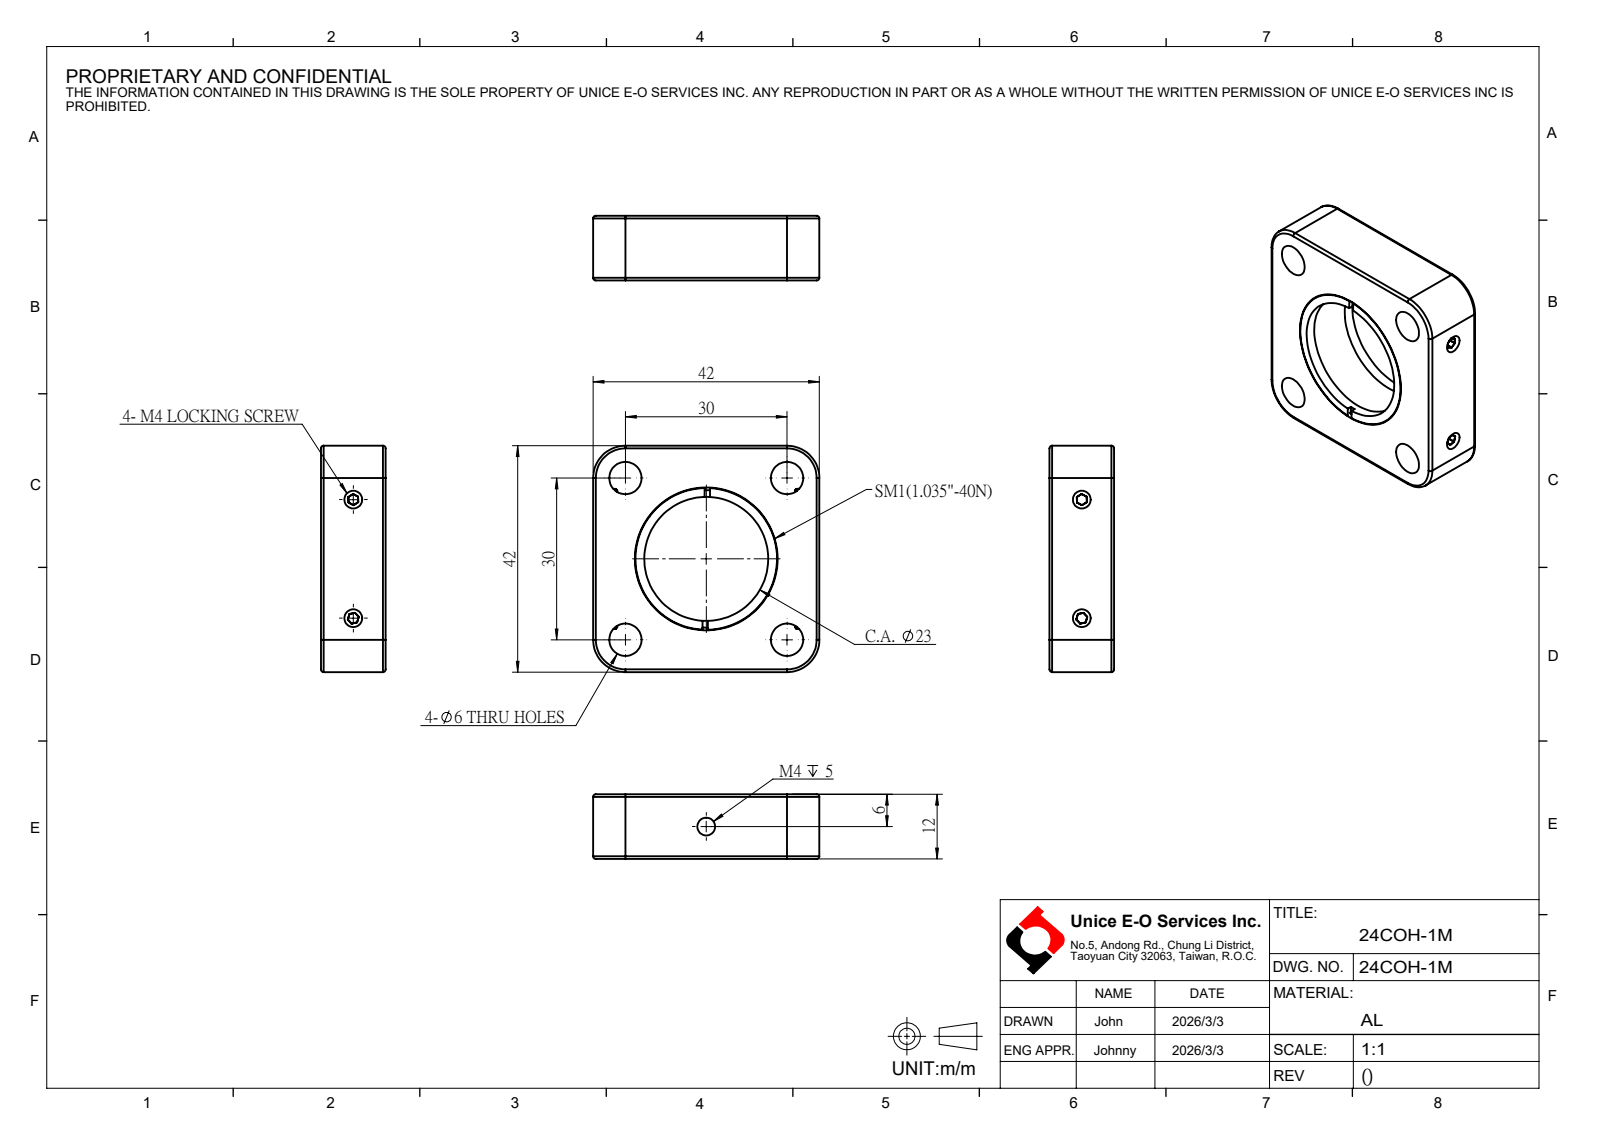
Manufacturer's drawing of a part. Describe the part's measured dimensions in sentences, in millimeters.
The part is named "24COH-1M". Its 3-D file was written by "SolidWorks 2024 (CONFIG_CONTROL_DESIGN)". It is 0 solids with 104 faces: 52 planar, 40 cylindrical and 12 other. Overall it measures 42 by 42 by 12 millimeters. Round holes: 4 of diameter 6, 3 of diameter 3.3, 1 of diameter 23, 1 of diameter 25.5. Round bosses or shafts: 1 of diameter 26.29. Partial cylindrical surfaces (rounded edges, fillets, slot ends): 8 of radius 0.5, 4 of radius 6. The main face-to-face distances are 12, 42, 2, 10, 8, 0.5, 41.5, 1.82, 41, 0.8. The hole center spacings are 21.21, 30, 42.43, 22.
